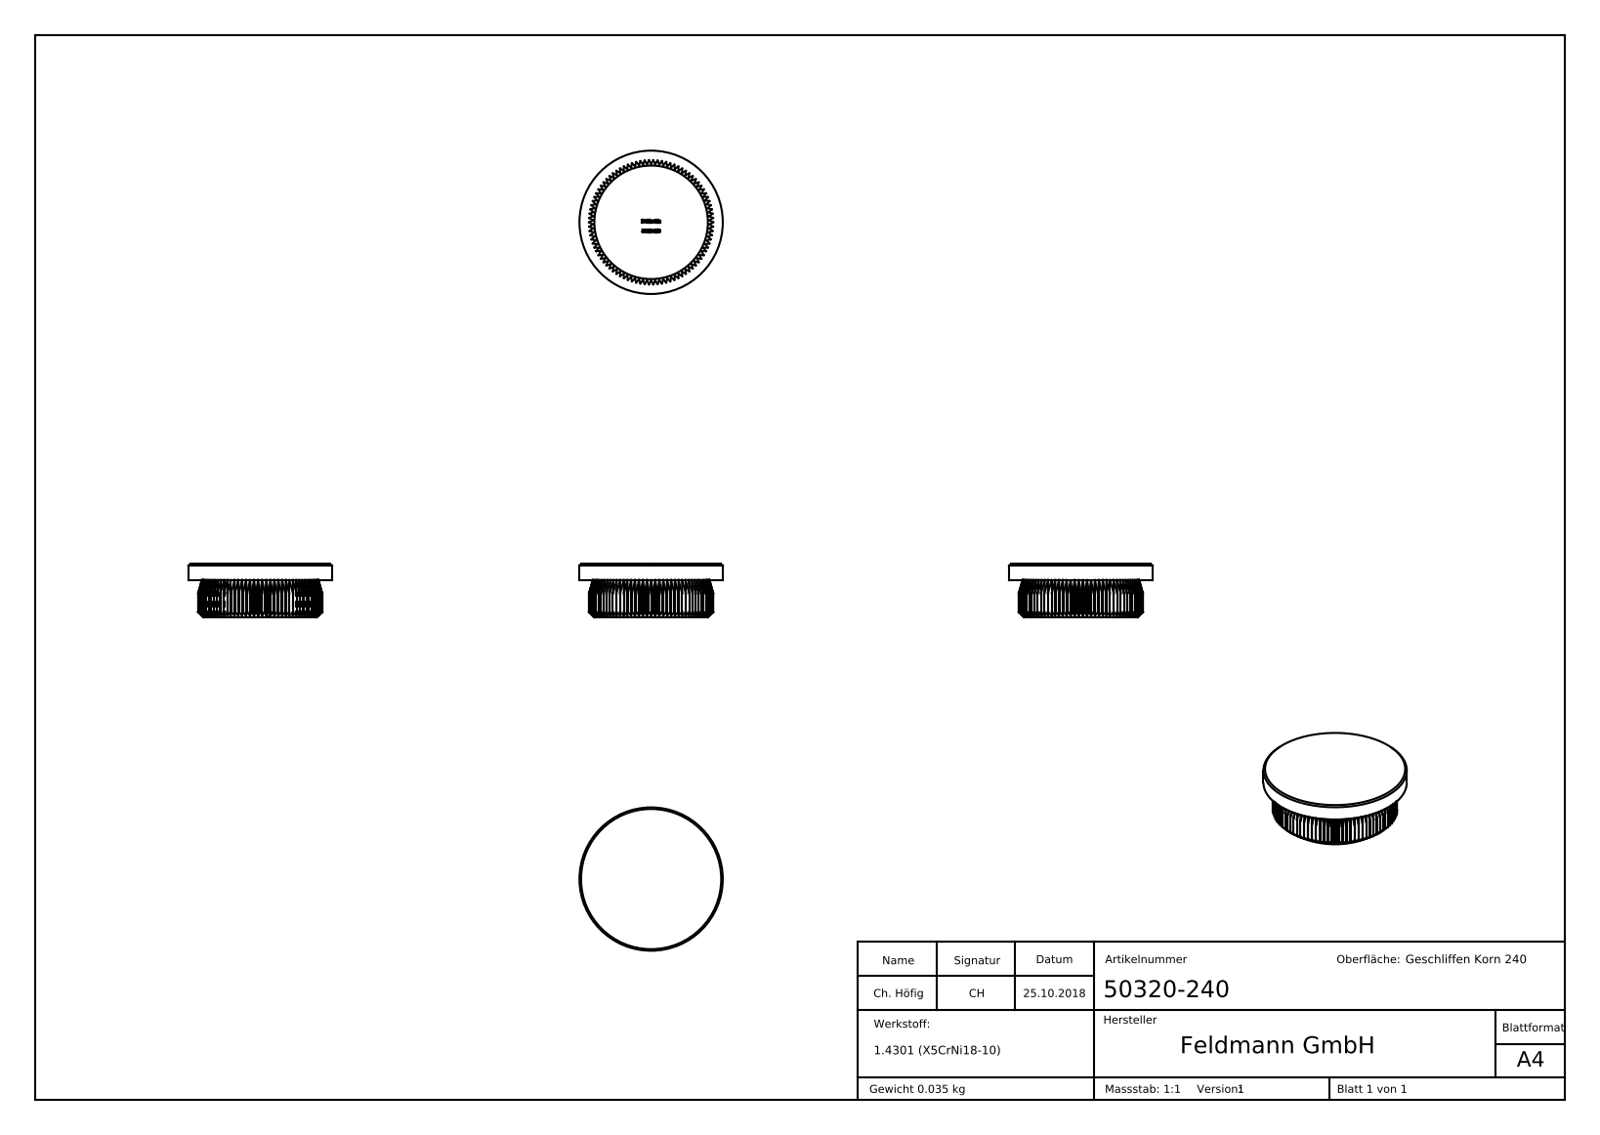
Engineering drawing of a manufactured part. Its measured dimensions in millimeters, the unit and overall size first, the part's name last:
Units: millimetres
Overall size (bounding box): 26.9 × 26.9 × 10
Round bosses / shafts (diameter × count): ⌀26.9 ×1
Partial cylindrical surfaces — rounded edges, fillets, slot ends (radius × count): R11.65 ×1
Main face-to-face distances: 10, 10.95, 10.94, 7, 3, 10.96, 6.9, 9.9, 3.77, 1.64
Volume: 4 472 mm³ · Surface area: 2 252 mm²
Bodies: 1 solid, 622 faces (321 planar, 92 cylindrical, 209 other)
Part name (STEP PRODUCT): 50320-240
STEP written by: SolidWorks 2015 (CONFIG_CONTROL_DESIGN)
